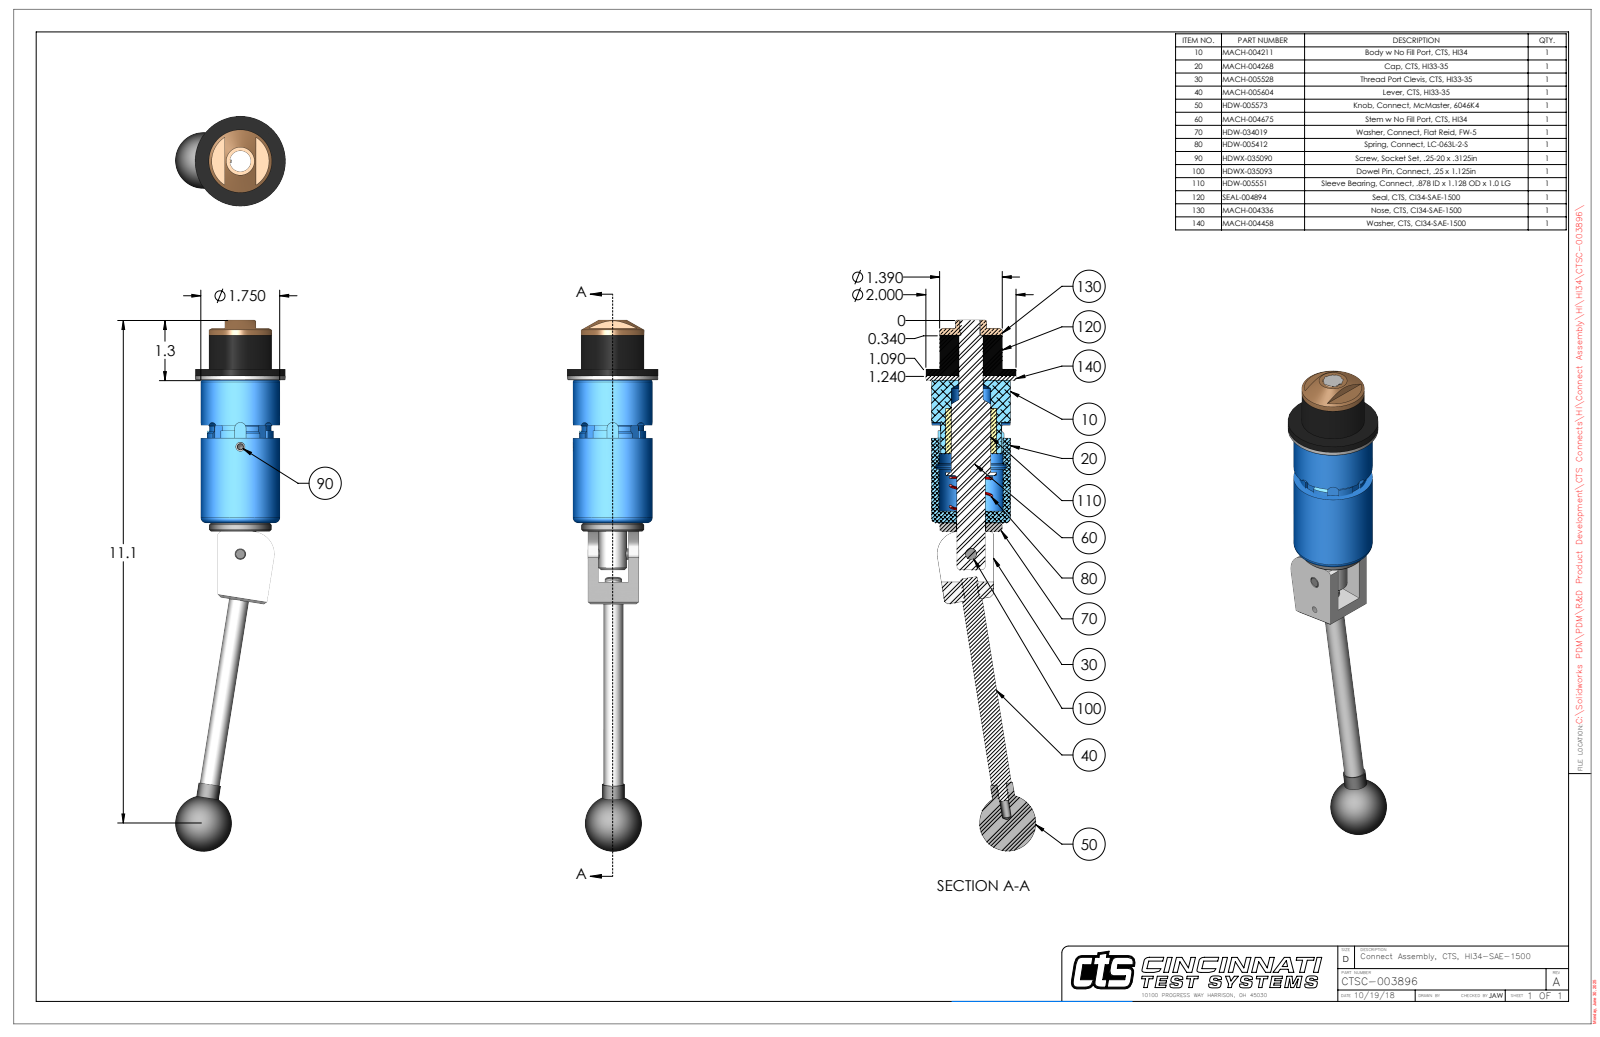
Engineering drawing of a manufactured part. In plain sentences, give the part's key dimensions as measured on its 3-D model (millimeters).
The part is named "CTSC-003896". Its 3-D file was written by "SolidWorks 2023 (AUTOMOTIVE_DESIGN)". It is 9 solids with 271 faces: 101 planar, 113 cylindrical and 57 other. Overall it measures 299 by 61.9 by 50.8 millimeters. Its volume is 212 000 cubic millimeters and its surface area 50 940 square millimeters. Round holes: 2 of diameter 5.1, 1 of diameter 3.8, 1 of diameter 6.3, 1 of diameter 6.4, 1 of diameter 8, 1 of diameter 10.7, 1 of diameter 13.5, 1 of diameter 13.7, 1 of diameter 13.9, 1 of diameter 16.1, 1 of diameter 16.7. Round bosses or shafts: 2 of diameter 12.7, 2 of diameter 11.2, 2 of diameter 6.4, 1 of diameter 50.8, 1 of diameter 44.5, 1 of diameter 35.3, 1 of diameter 35.1, 1 of diameter 15.9. Partial cylindrical surfaces (rounded edges, fillets, slot ends): 4 of radius 3.2, 2 of radius 0.7, 1 of radius 12.7, 1 of radius 18, 1 of radius 18.9, 1 of radius 20.5. The main face-to-face distances are 2.4, 22.9, 25.2, 105.5, 82.7, 80.3, 28.4, 19.1, 3.8, 6.2. The hole center spacings are 18.8, 60.4, 79.1.
